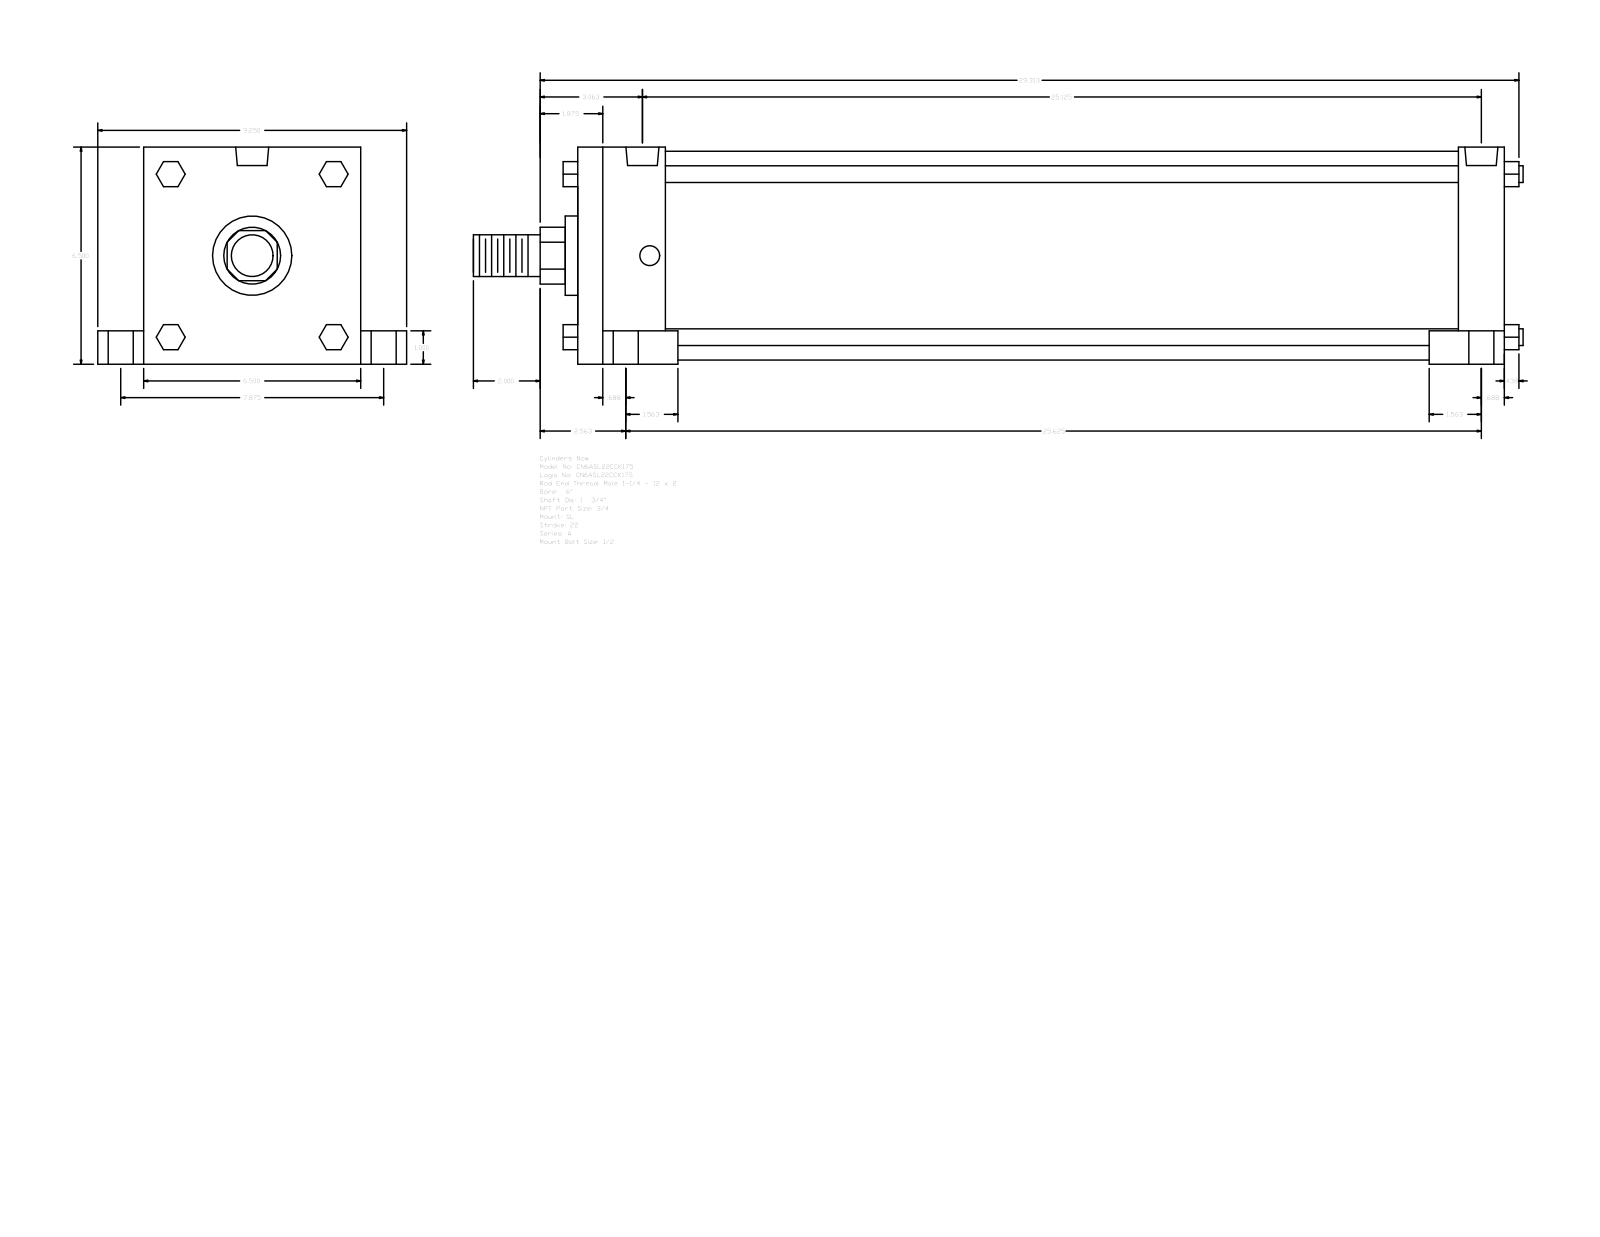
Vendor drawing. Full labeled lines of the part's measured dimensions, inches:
Part name (STEP PRODUCT): A_SL__0600_1.75
STEP written by: GSSL Pune (CONFIG_CONTROL_DESIGN)
Units: inches
Bodies: 0 solids, 150 faces (114 planar, 36 cylindrical, 0 other)
Overall size (bounding box): 31.437 × 9.25 × 6.5
Round holes (diameter × count): ⌀0.594 ×4, ⌀0.75 ×4, ⌀1 ×4, ⌀0.989 ×2
Round bosses / shafts (diameter × count): ⌀0.5 ×4, ⌀6.25 ×1, ⌀2.375 ×1, ⌀1.75 ×1, ⌀1.25 ×1
Partial cylindrical surfaces — rounded edges, fillets, slot ends (radius × count): R0.852 ×1
Main face-to-face distances: 6.5, 27.75, 1.375, 2.625, 25.125, 26.375, 23.75, 1, 5.5, 7.875
Hole centre spacings: 0.219, 3.937, 3.943, 3.969, 4.002, 7.875, 24.687, 24.906
